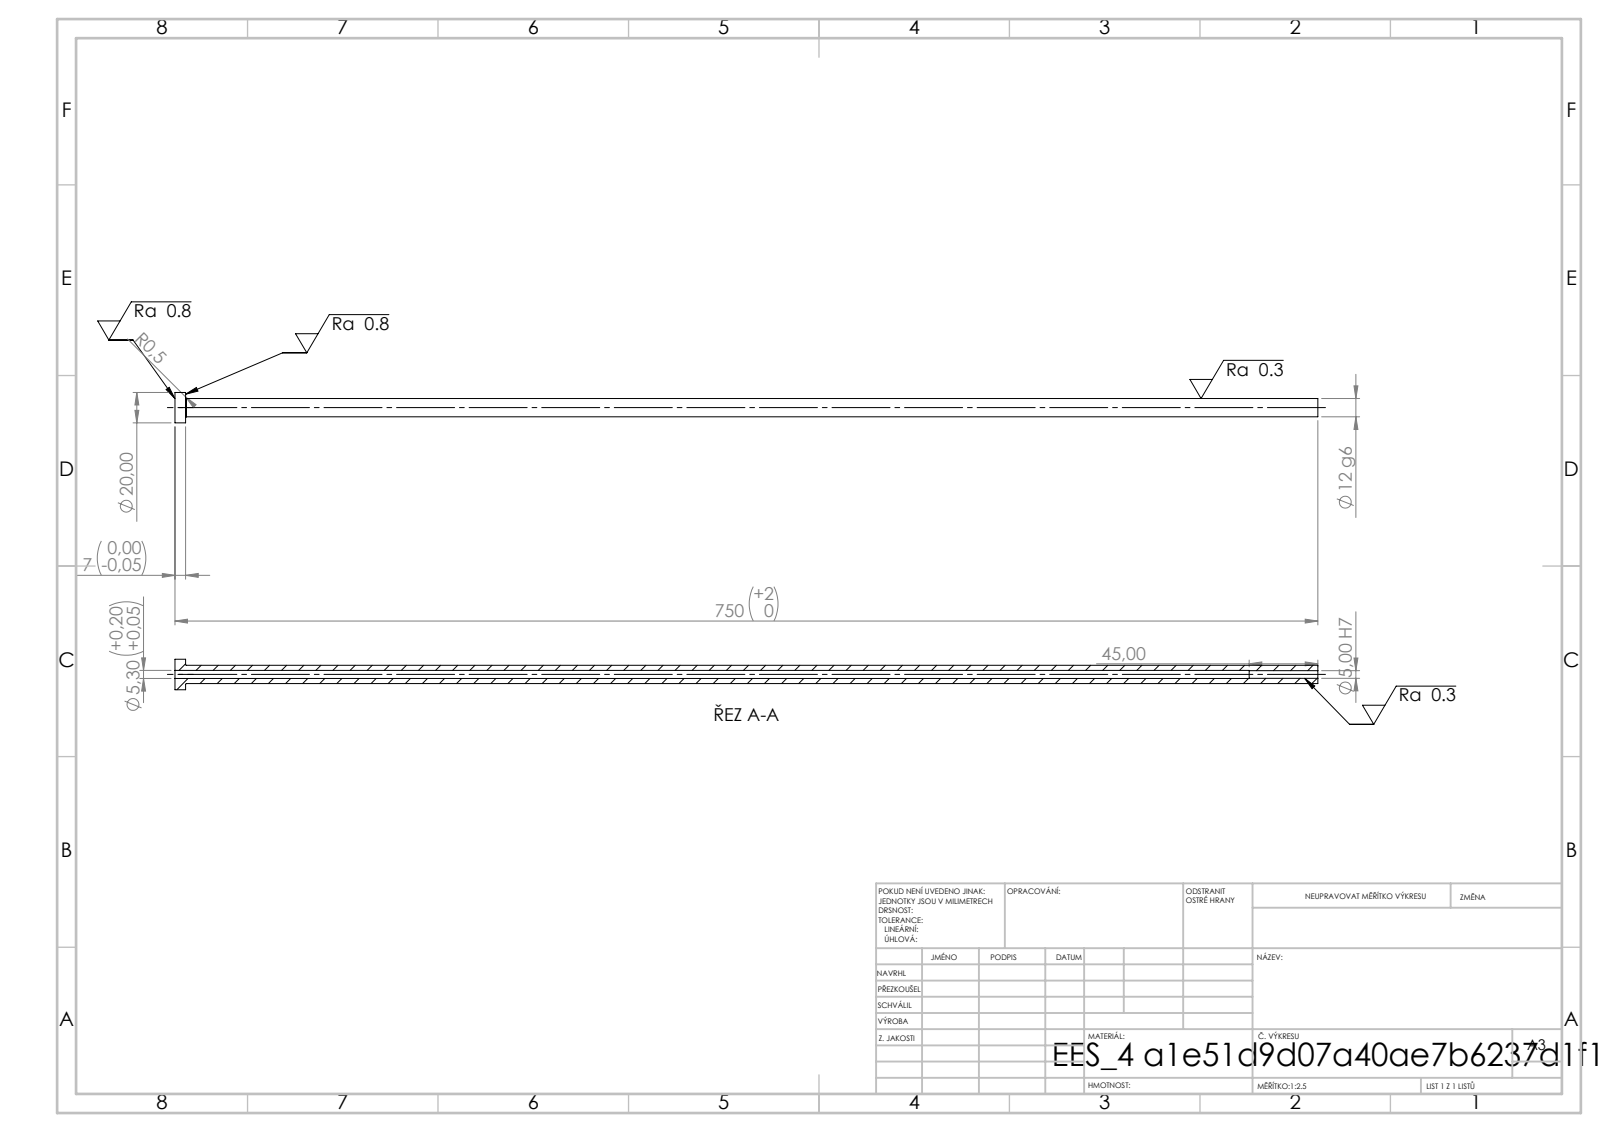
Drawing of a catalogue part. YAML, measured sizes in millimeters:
step_written_by: "SolidWorks 2019 (CONFIG_CONTROL_DESIGN)"
units: millimeters
bodies: {solids: 1, faces: 14, planar: 4, cylindrical: 8, other: 2}
overall_size: [750, 20, 20]
volume: 69795
surface_area: 41477
round_holes:
  - {diameter: 5, count: 1}
  - {diameter: 5.3, count: 1}
round_bosses_or_shafts:
  - {diameter: 20, count: 1}
  - {diameter: 12, count: 1}
face_to_face_distances: [7, 750, 743, 705, 698, 45]
